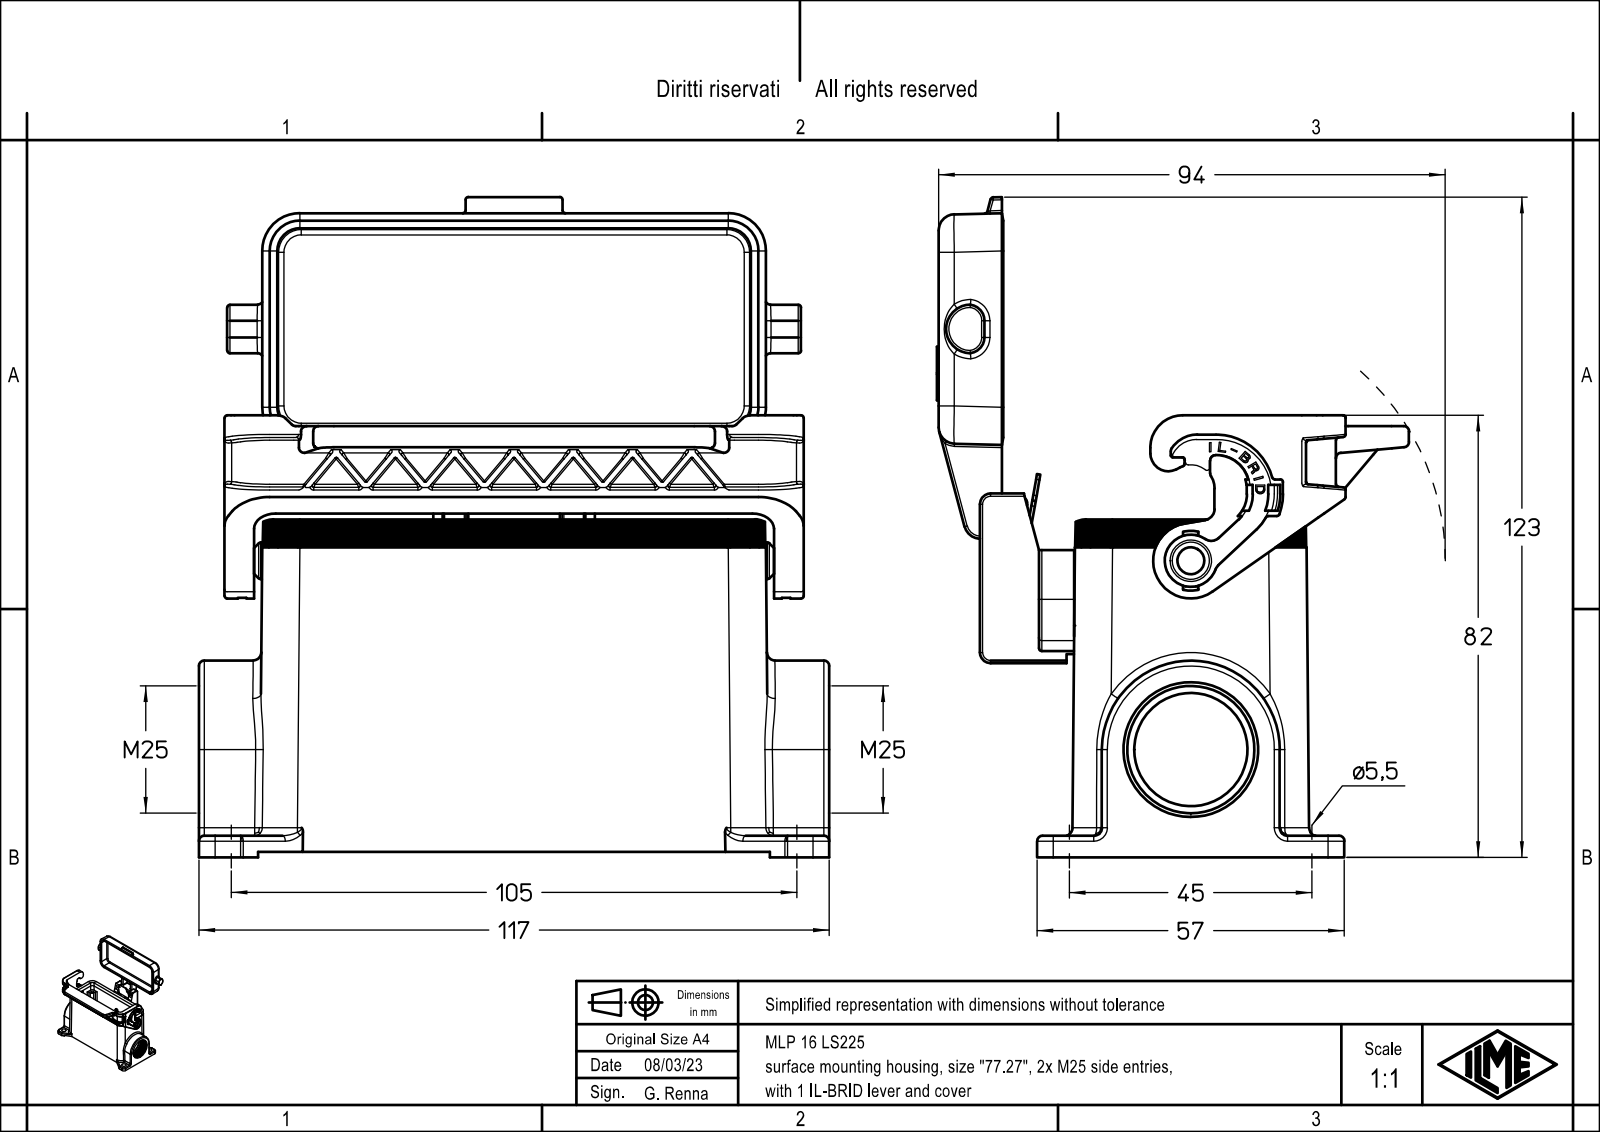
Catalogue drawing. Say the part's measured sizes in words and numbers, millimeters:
The part is named "MLP 16 LS225". Its 3-D file was written by "Creo Elements/Direct Modeling 20.1B 02-Apr-2019 (C) Parametric Technology GmbH (AUTOMOTIVE_DESIGN)". It is 1 solid with 1431 faces: 818 planar, 406 cylindrical and 207 other. Overall it measures 122.49 by 117 by 87.8 millimeters. Its volume is 135 475 cubic millimeters and its surface area 80 378 square millimeters. Round holes: 4 of diameter 3, 4 of diameter 3.5, 4 of diameter 5.5, 1 of diameter 3.25, 1 of diameter 4.2, 1 of diameter 5.4, 1 of diameter 7.7, 1 of diameter 21, 1 of diameter 23.6. Round bosses or shafts: 1 of diameter 8.4, 1 of diameter 6.9, 1 of diameter 6.8, 1 of diameter 5.2, 1 of diameter 4, 1 of diameter 3.2. Partial cylindrical surfaces (rounded edges, fillets, slot ends): 28 of radius 0.5, 27 of radius 0.1, 27 of radius 1, 23 of radius 0.2, 23 of radius 3, 17 of radius 0.17, 16 of radius 0.33, 15 of radius 1.5. The main face-to-face distances are 2, 3, 2.8, 69.75, 71.75, 10.25, 106.75, 1, 79, 76. The hole center spacings are 16.43, 38.54, 91.69, 98.09, 27, 45, 77.5, 82.07.
